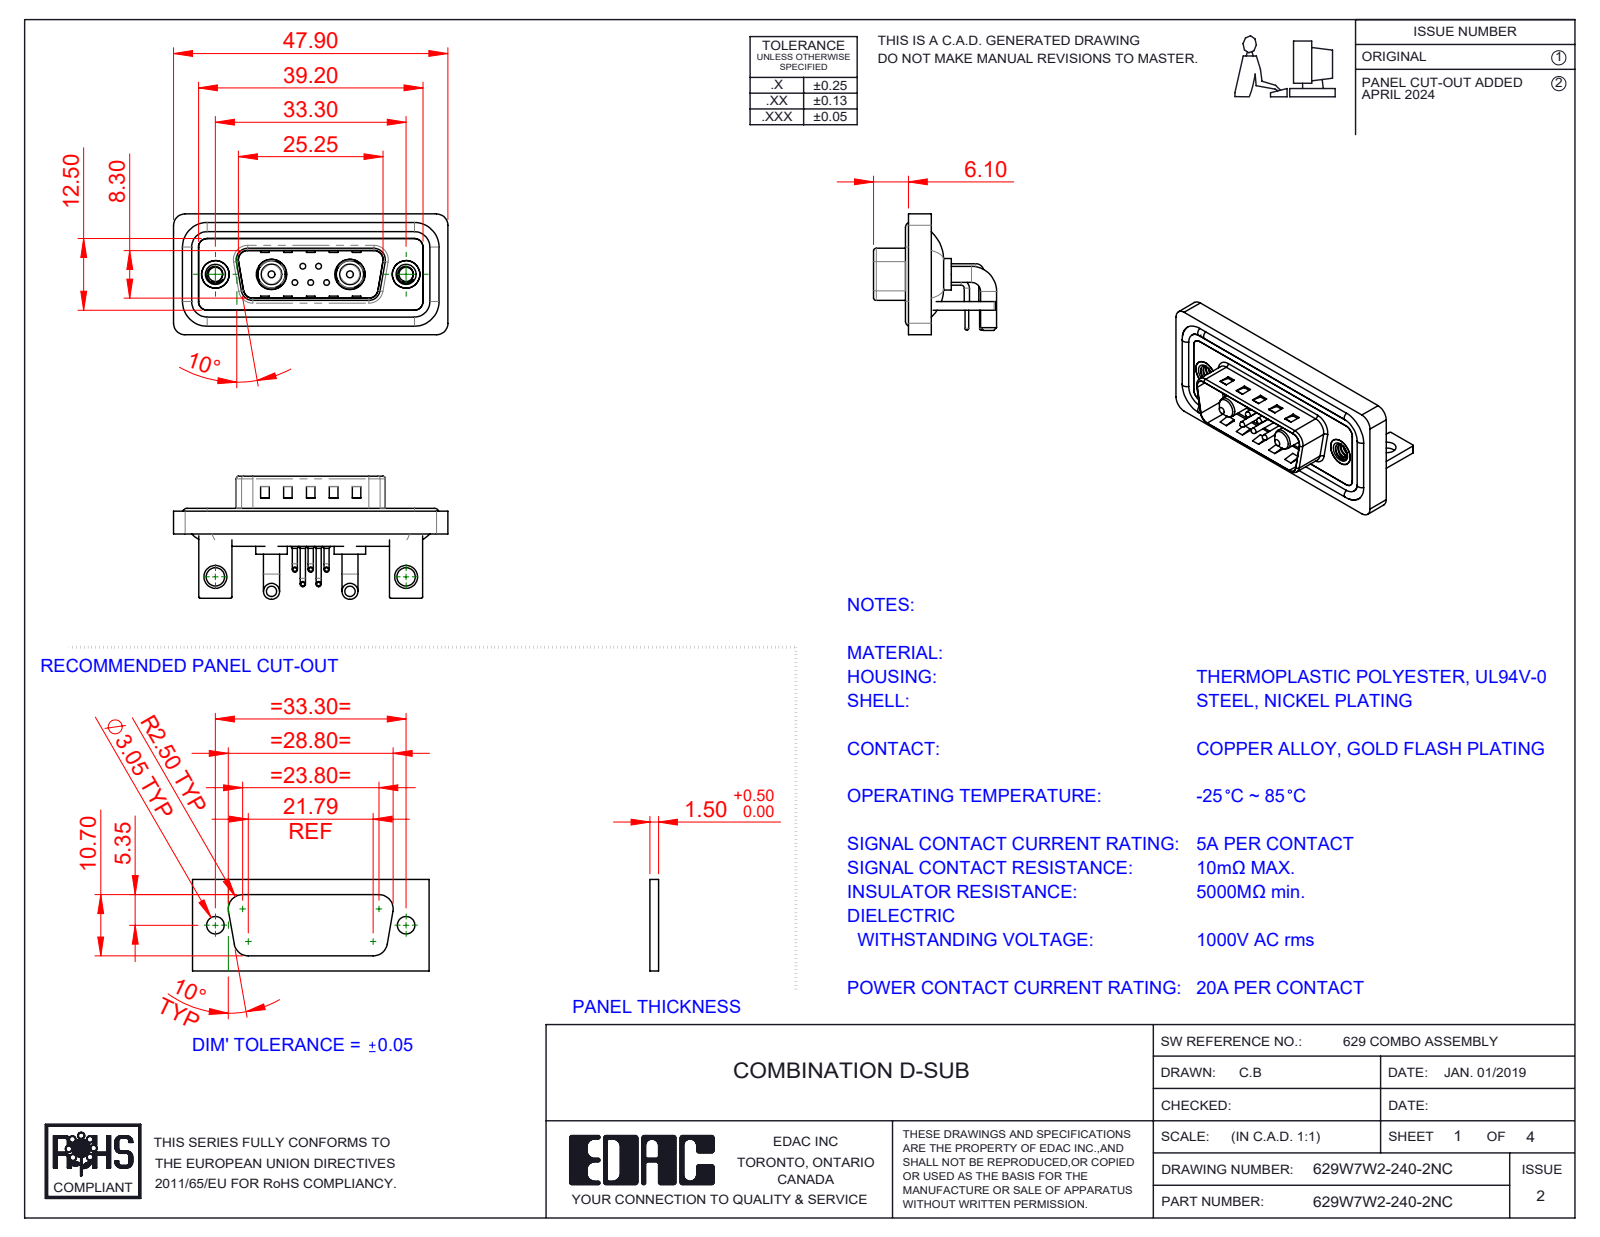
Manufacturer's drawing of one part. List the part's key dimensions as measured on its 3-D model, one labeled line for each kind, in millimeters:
Part name (STEP PRODUCT): 629Combo Shell Front_15 Contacts; 629Combo Shell Rear_15 Contacts; 629Combo Waterproof Housing_15 Contacts; 629Combo Stabilizer Bracket (+6 more)
STEP written by: SolidWorks 2023 (CONFIG_CONTROL_DESIGN)
Units: millimetres
Bodies: 18 solids, 1121 faces (537 planar, 424 cylindrical, 160 other)
Overall size (bounding box): 47.9 × 21.5 × 21.1
Volume: 5 952 mm³ · Surface area: 9 729 mm²
Round holes (diameter × count): ⌀0.75 ×5, ⌀1.6 ×5, ⌀2 ×5, ⌀2.5 ×2, ⌀3.2 ×2, ⌀4 ×2, ⌀4.8 ×2, ⌀4.85 ×2, ⌀5 ×2, ⌀5.3 ×2
Round bosses / shafts (diameter × count): ⌀0.9 ×10, ⌀1.5 ×5, ⌀1 ×5, ⌀0.65 ×5, ⌀2.8 ×4, ⌀1.6 ×4, ⌀5.5 ×2, ⌀5.2 ×2
Partial cylindrical surfaces — rounded edges, fillets, slot ends (radius × count): R2 ×21, R1.5 ×18, R0.25 ×16, R0.5 ×9, R1.6 ×8, R1.01 ×5, R0.6 ×4, R0.65 ×4
Main face-to-face distances: 0.4, 1.5, 0.8, 2.9, 2.1, 1.1, 1.6, 1.2, 3.7, 4.5
Hole centre spacings: 3.16, 2.77, 9.8, 23.5, 33.3, 4.31, 4.33, 5.03
